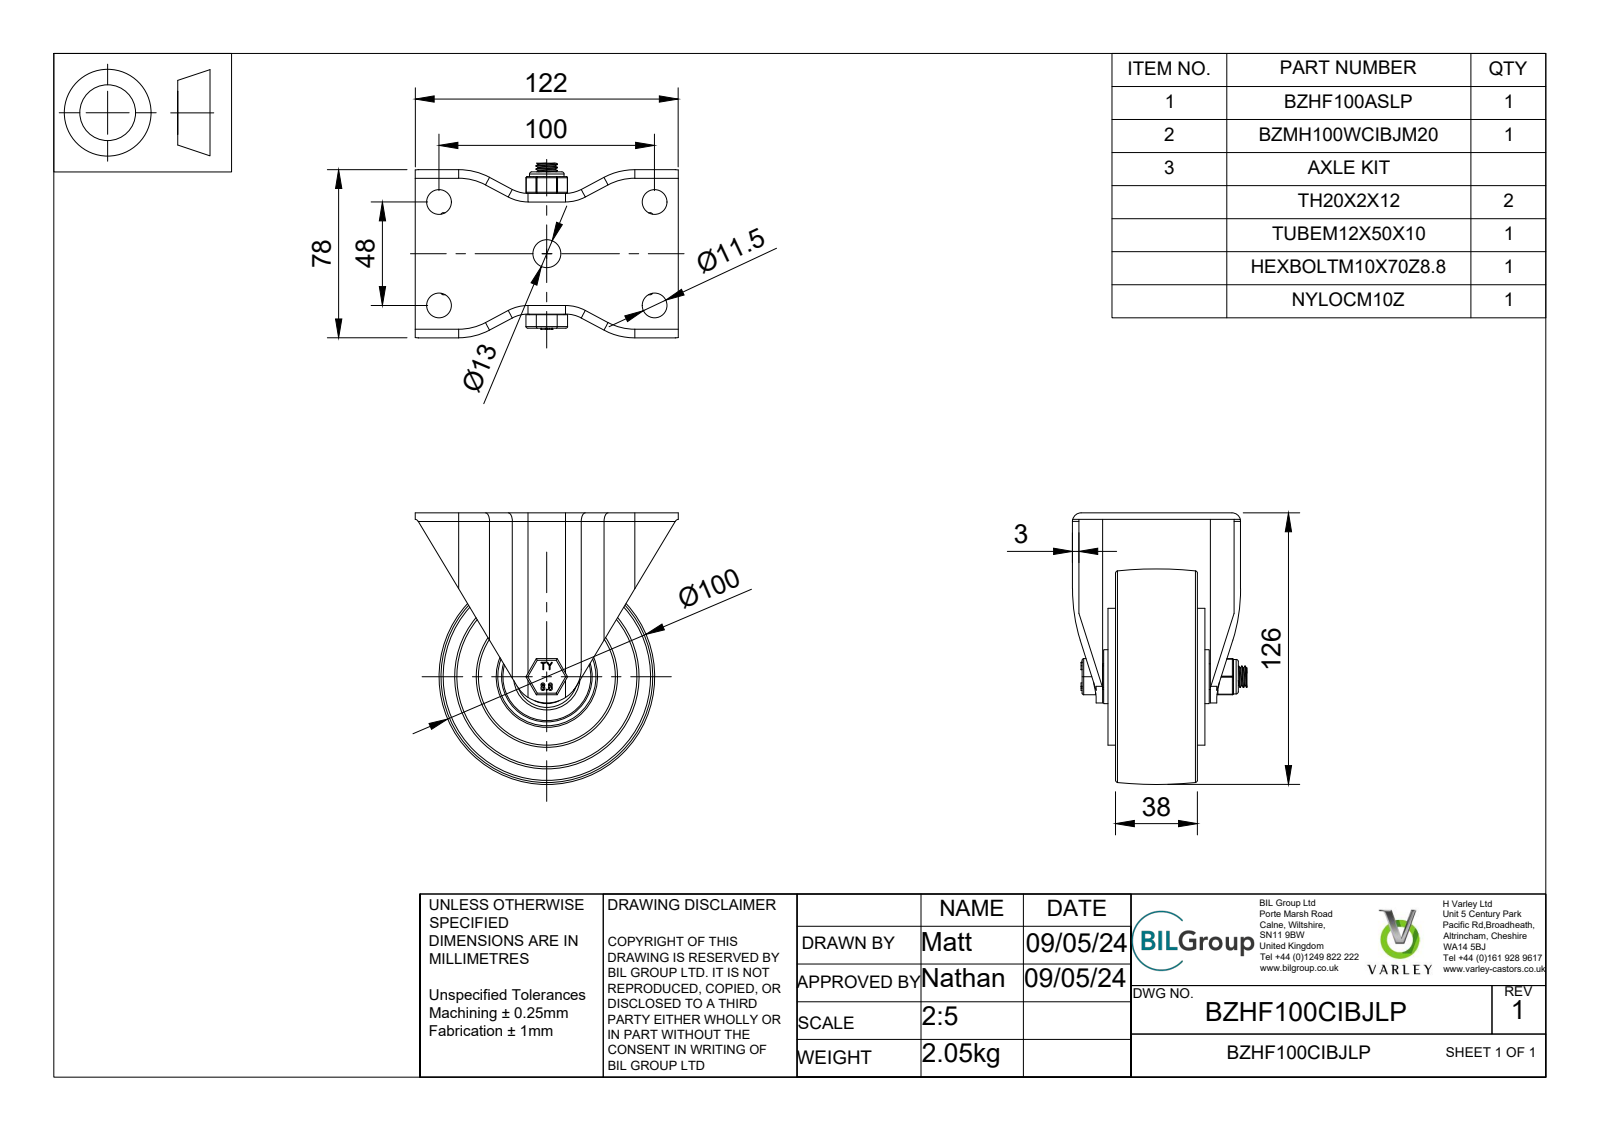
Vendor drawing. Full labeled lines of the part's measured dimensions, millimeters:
Part name (STEP PRODUCT): BZHF100CIBJLP v3; BZHF100ASLP - 50 v1; ZINC PLATED PRESSED STEEL BRACKET; BZMH100WCIBJM20 v1 (+7 more)
STEP written by: Autodesk Translation Framework v12.20.1.177 (AUTOMOTIVE_DESIGN)
Units: millimetres
Bodies: 35 solids, 1013 faces (402 planar, 197 cylindrical, 414 other)
Overall size (bounding box): 126 × 122 × 81
Volume: 274 892 mm³ · Surface area: 135 880 mm²
Round holes (diameter × count): ⌀11.5 ×4, ⌀10 ×1, ⌀10.2 ×1, ⌀10.8 ×1, ⌀12 ×1, ⌀12.2 ×1, ⌀13 ×1, ⌀20 ×1, ⌀28.5 ×1, ⌀30.8 ×1, ⌀40.3 ×1, ⌀40.5 ×1
Round bosses / shafts (diameter × count): ⌀63.5 ×1, ⌀40.8 ×1, ⌀31.3 ×1, ⌀27 ×1, ⌀25 ×1, ⌀23 ×1, ⌀19.8 ×1, ⌀16 ×1
Partial cylindrical surfaces — rounded edges, fillets, slot ends (radius × count): R0.5 ×18, R4 ×8, R0.75 ×6, R15.5 ×4, R30.5 ×4, R2 ×2, R16 ×1, R16.5 ×1
Main face-to-face distances: 3, 14, 27.5, 13.5, 47.5, 20, 17.5, 30, 17, 31
Hole centre spacings: 55.46, 48, 100, 110.92
